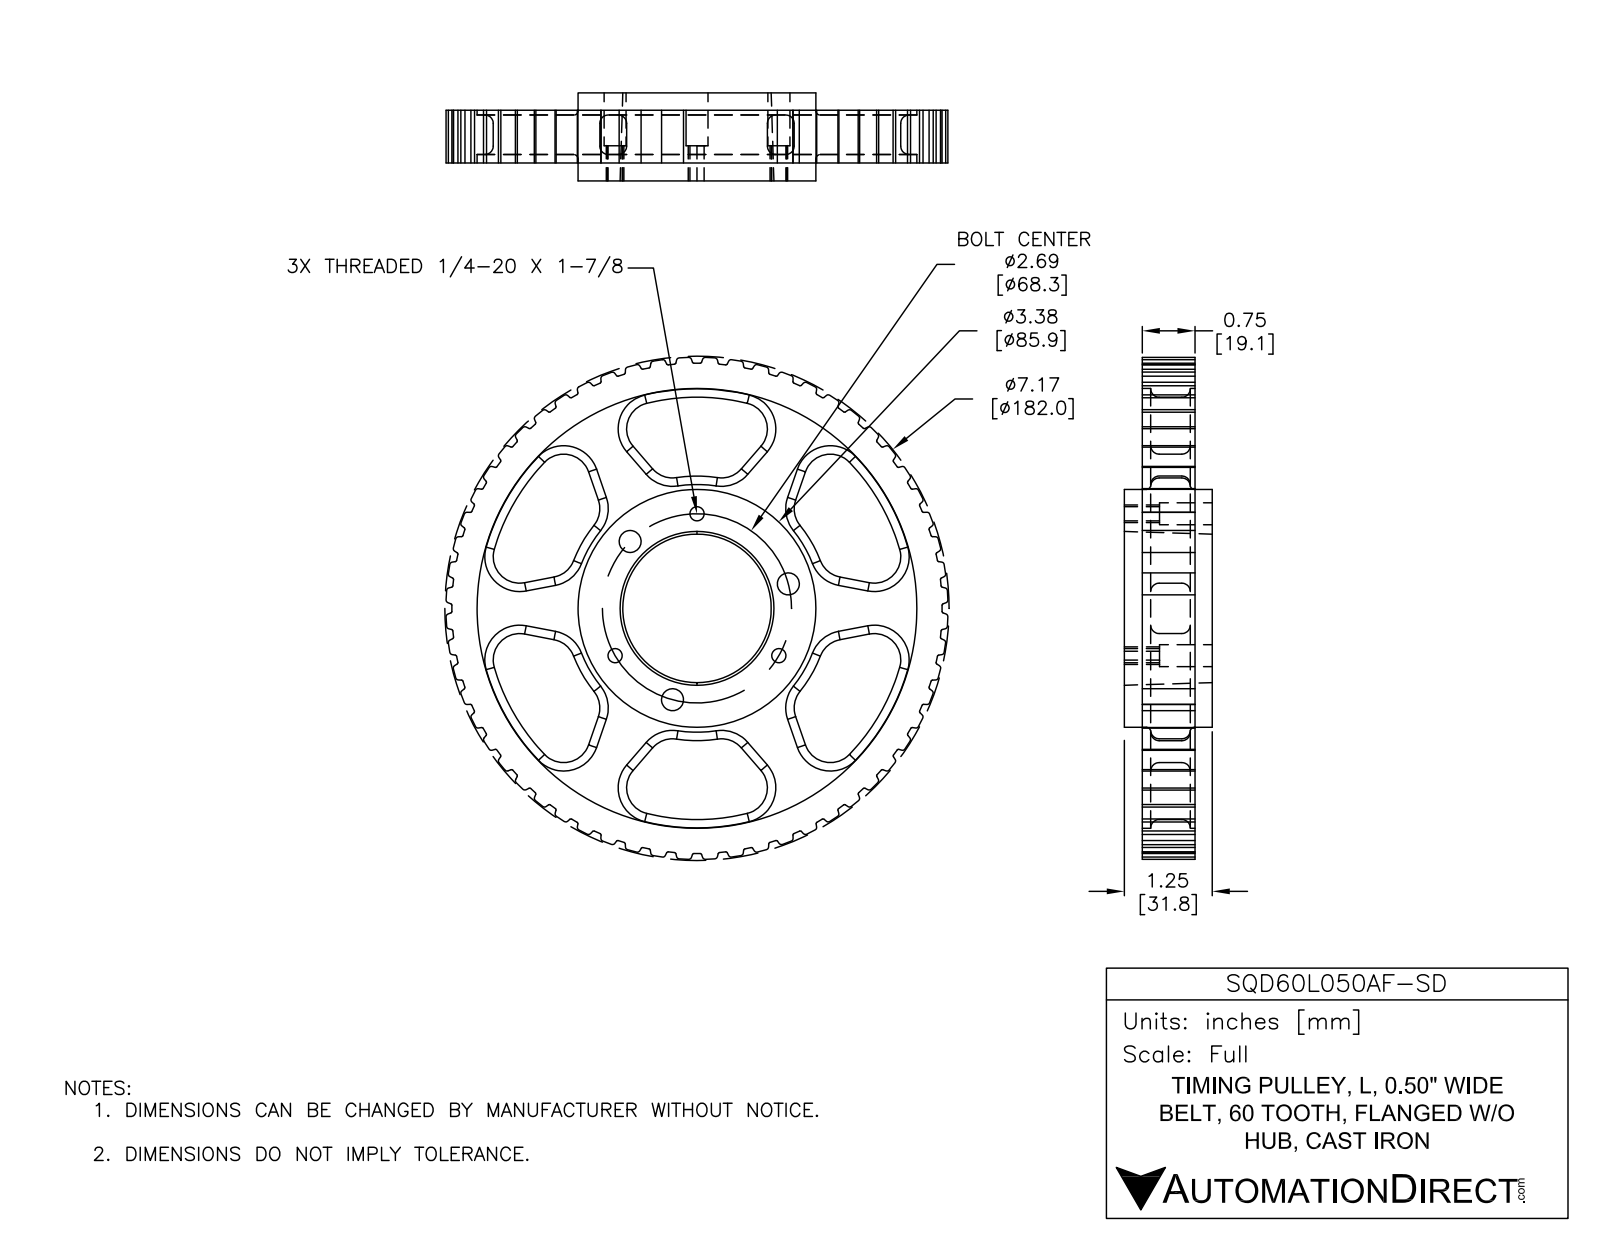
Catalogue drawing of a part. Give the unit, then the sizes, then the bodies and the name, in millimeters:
Units: millimetres
Overall size (bounding box): 181.1 × 181.1 × 31.8
Round holes (diameter × count): ⌀8 ×6, ⌀5.1 ×3, ⌀152.4 ×1
Round bosses / shafts (diameter × count): ⌀92.1 ×1
Partial cylindrical surfaces — rounded edges, fillets, slot ends (radius × count): R0.5 ×120, R1 ×120, R2.5 ×24, R4.8 ×24, R49.1 ×1, R73 ×1, R90.6 ×1
Main face-to-face distances: 6.4, 25.4, 9.7, 22.1, 3.3, 15.7, 19.1, 31.8, 12.4, 177
Hole centre spacings: 34.1, 59.1, 59.1, 67.7, 26.1, 41.6, 26.1, 34.1
Volume: 331 300 mm³ · Surface area: 73 100 mm²
Bodies: 1 solid, 735 faces (201 planar, 440 cylindrical, 94 other)
Part name (STEP PRODUCT): SQD60L050AF-SD
STEP written by: SolidWorks 2014 (AUTOMOTIVE_DESIGN)
